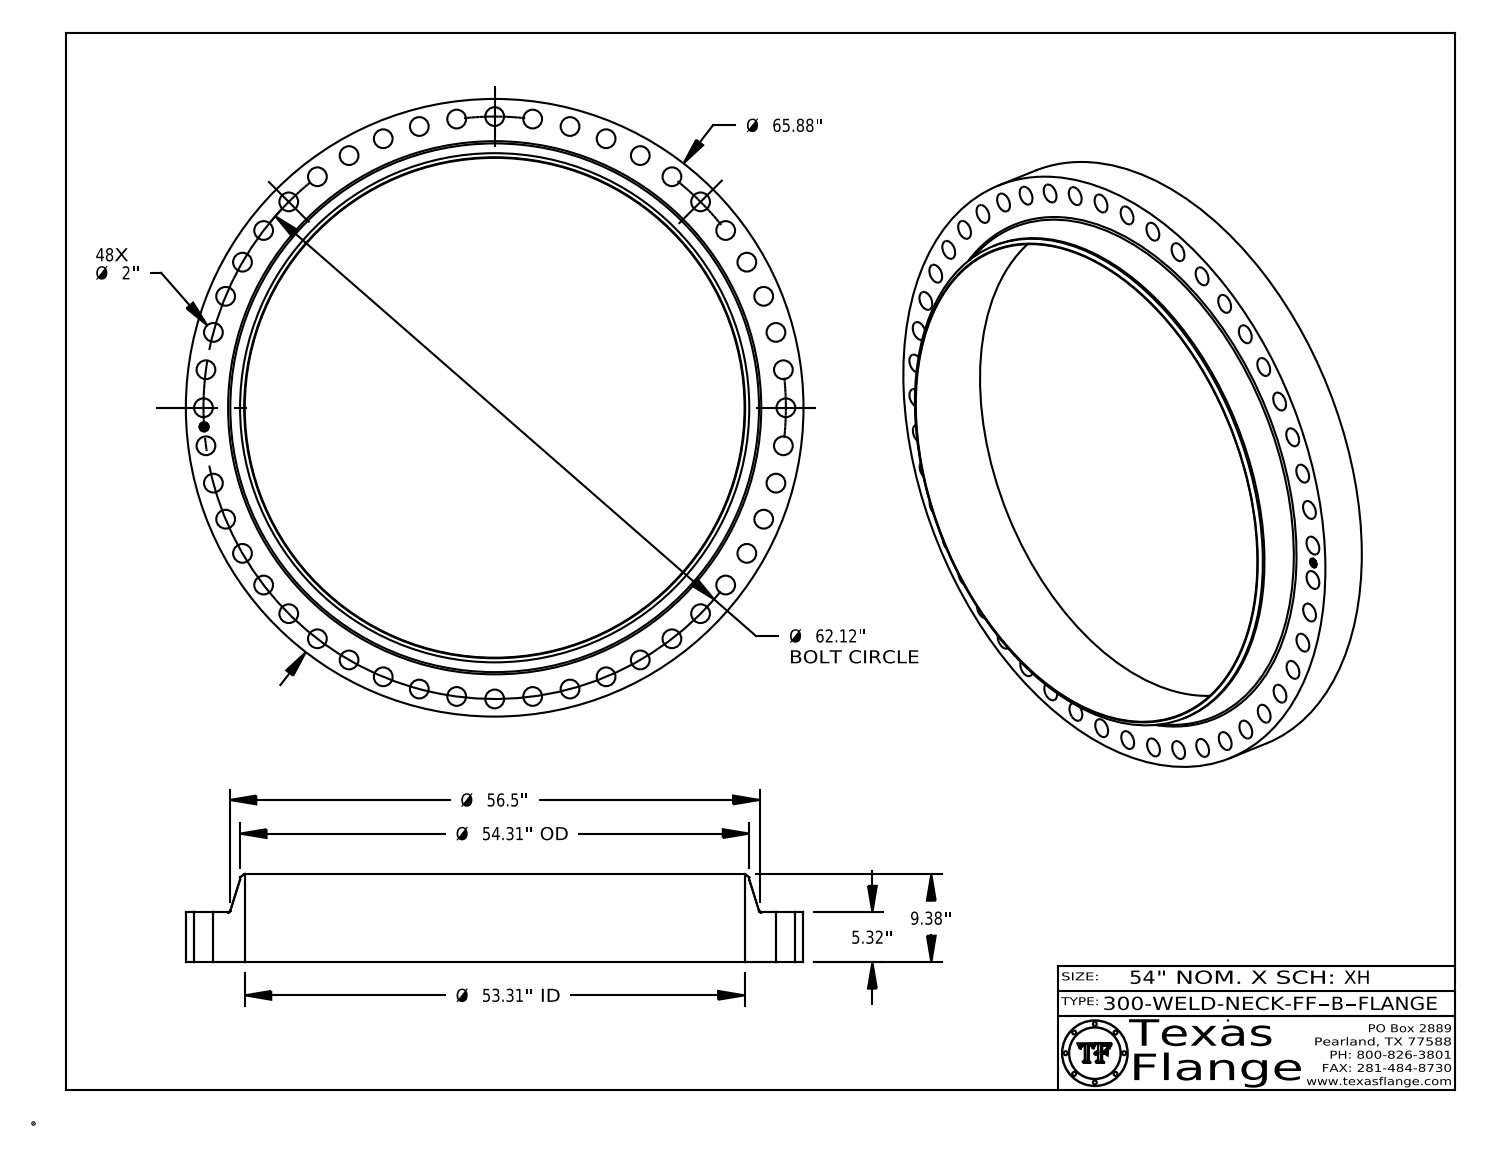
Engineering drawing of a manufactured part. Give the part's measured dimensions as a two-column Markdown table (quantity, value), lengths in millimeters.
| quantity | value |
| --- | --- |
| part name | 300-WELD-NECK-FF, Series B |
| STEP written by | CATIA V5 STEP AP214 (AUTOMOTIVE_DESIGN) |
| units | millimeters |
| bodies | 1 solid, 496 faces (368 planar, 122 cylindrical, 6 other) |
| overall size | 1673.4 × 1673.4 × 238.3 |
| volume | 100 300 000 mm³ |
| surface area | 4 403 000 mm² |
| round holes (diameter × count) | 50.8 × 48, 25.4 × 1, 1354.1 × 1 |
| round bosses / shafts (diameter × count) | 1.5 × 8, 1673.4 × 1, 1379.5 × 1, 20 × 1 |
| main face-to-face distances | 135.1, 238.3, 103.1, 0.4, 134.7, 103.5, 7.6, 7.4, 0.5, 1.4 |
| hole center spacings | 788.9, 205.9, 103.2, 1494.1, 1547.5, 1524.1, 507.2, 1415.1 |
